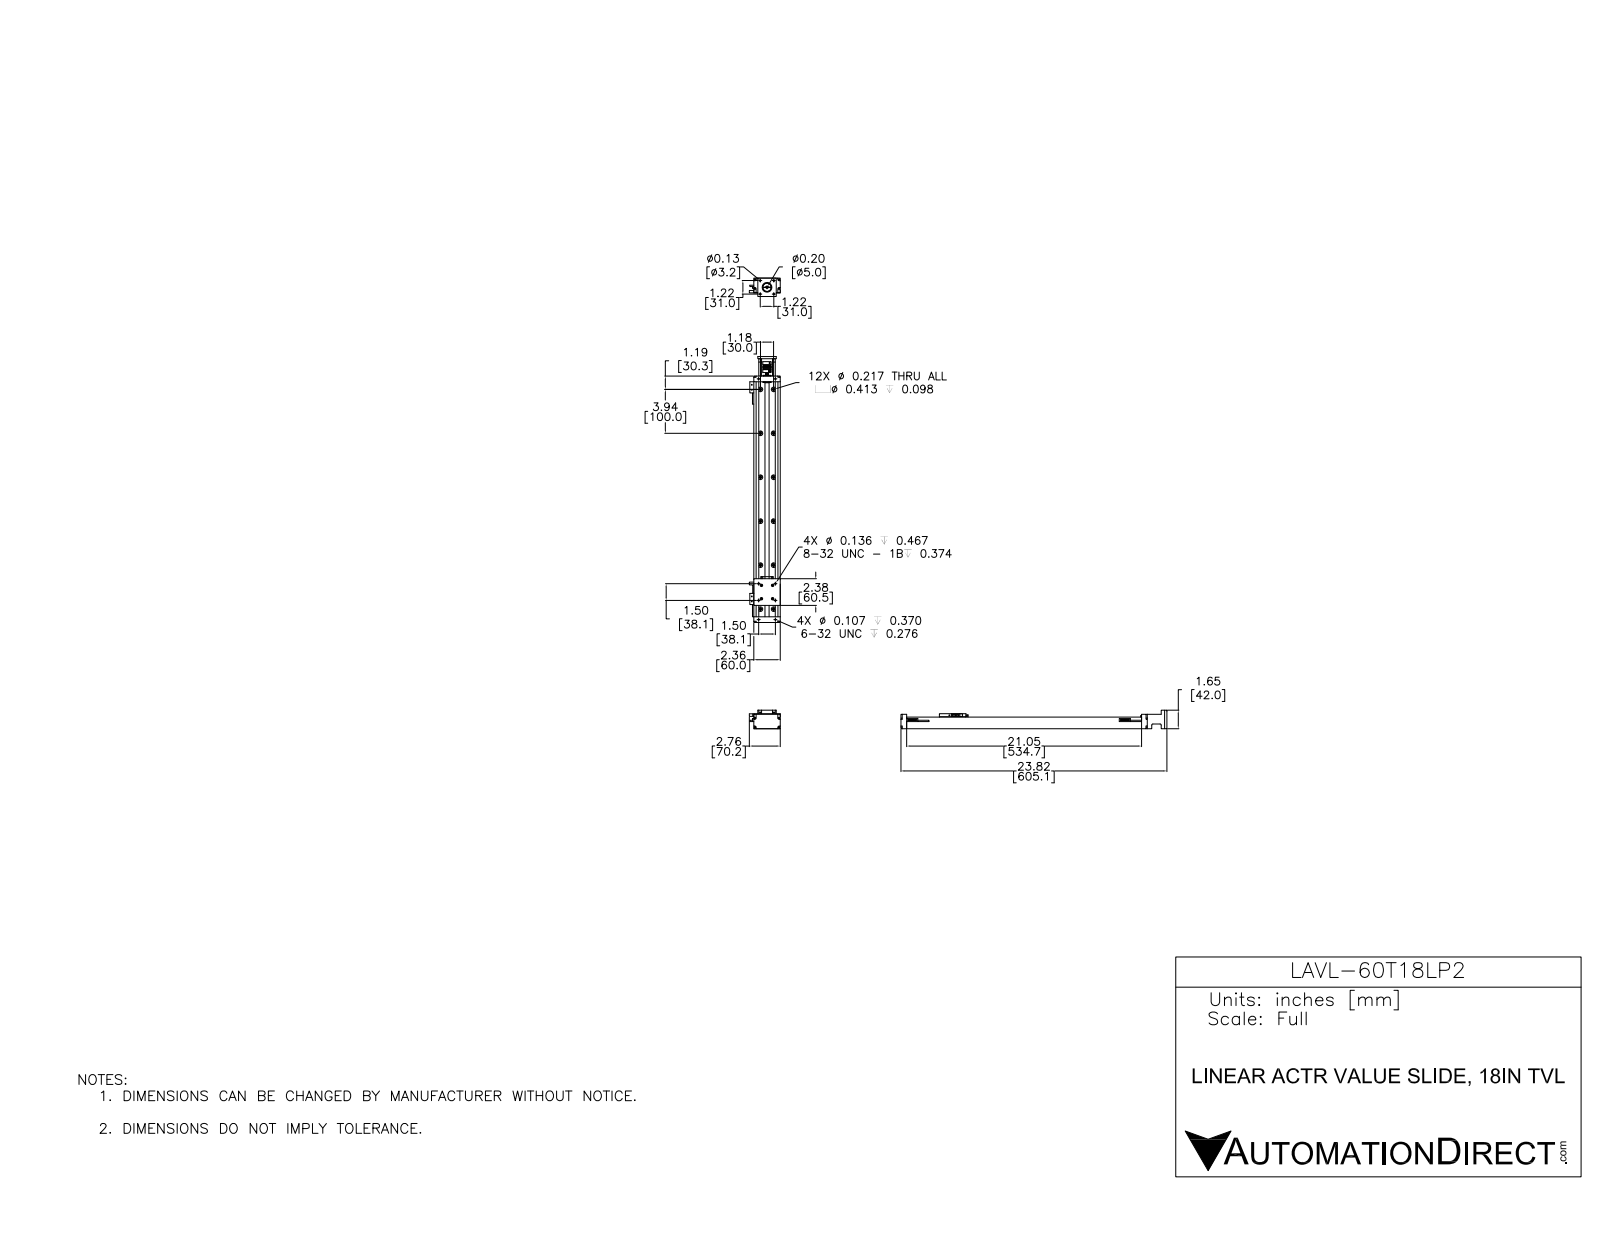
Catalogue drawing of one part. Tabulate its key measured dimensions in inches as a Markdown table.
| quantity | value |
| --- | --- |
| part name | LAVL-60T18LP2-RAIL; LAVL-60T18LP2; LAVL-60T06LP2-CAR |
| STEP written by | SolidWorks 2015 (AUTOMOTIVE_DESIGN) |
| units | inches |
| bodies | 19 solids, 907 faces (336 planar, 400 cylindrical, 171 other) |
| overall size | 23.824 × 2.762 × 1.654 |
| volume | 30.78 in³ |
| surface area | 369 in² |
| round holes (diameter × count) | 0.129 × 12, 0.217 × 12, 0.413 × 12, 0.107 × 10, 0.089 × 6, 0.136 × 6, 0.086 × 4, 0.12 × 4, 0.125 × 4, 0.125 × 4, 0.15 × 4, 0.219 × 4 |
| round bosses / shafts (diameter × count) | 0.22 × 4, 0.209 × 4, 0.157 × 2, 0.748 × 1, 0.69 × 1, 0.673 × 1, 0.625 × 1, 0.508 × 1 |
| partial cylindrical surfaces (radius × count) | 0.109 × 8, 0.047 × 4, 0.211 × 4, 0.266 × 4, 0.047 × 3, 0.188 × 3, 0.057 × 2, 0.062 × 2 |
| main face-to-face distances | 0.2, 2.162, 2.362, 1.962, 0.445, 0.645, 1.044, 0.844, 0.399, 0.512 |
| hole center spacings | 2.162, 1.089, 2.316, 3.937, 4.11, 1.181, 1.22, 1.289 |
